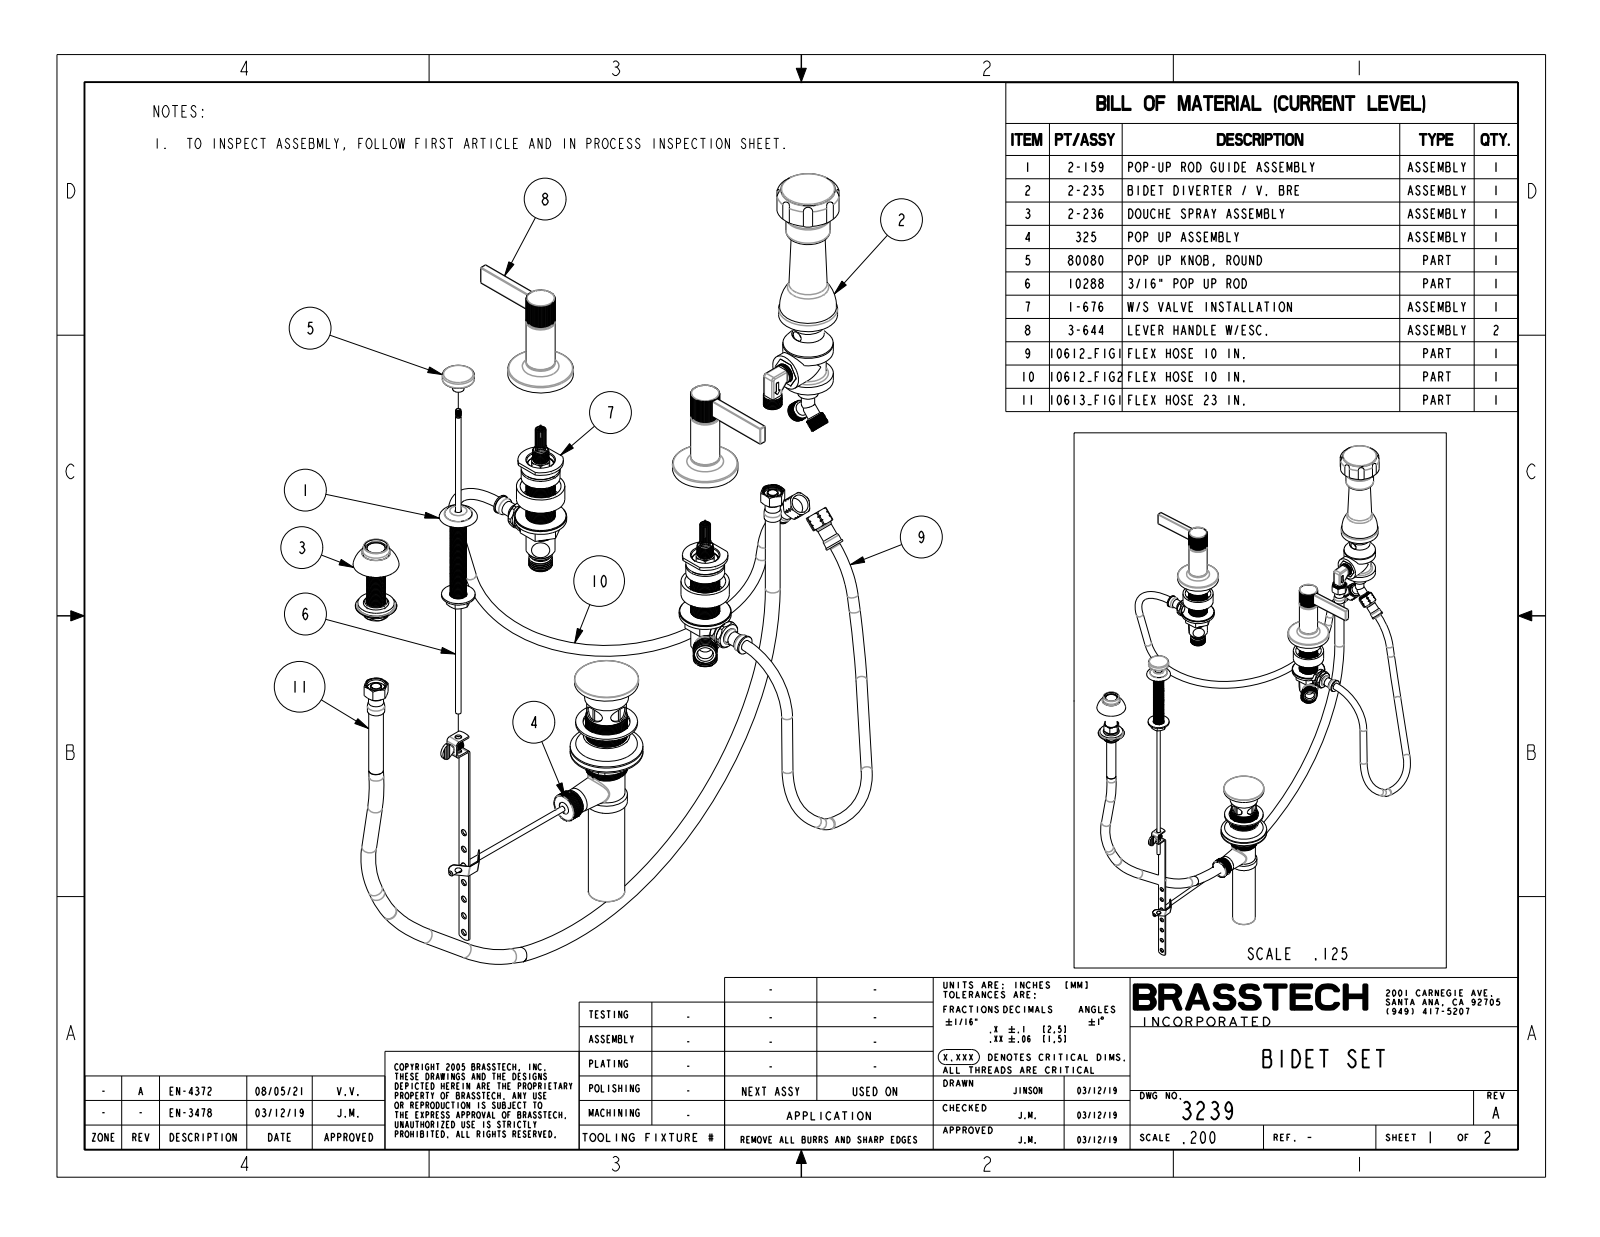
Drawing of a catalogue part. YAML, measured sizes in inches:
part_name: "10078; 2-159_ASM; 91093; 10600 (+8 more)"
step_written_by: "CREO PARAMETRIC BY PTC INC, 2018400 (CONFIG_CONTROL_DESIGN)"
units: inches
bodies: {solids: 39, faces: 3429, planar: 1238, cylindrical: 1397, other: 794}
overall_size: [22.855, 13.6, 5.373]
volume: 10.96
surface_area: 279.4
round_holes:
  - {diameter: 0.11, count: 4}
  - {diameter: 0.15, count: 3}
  - {diameter: 0.6, count: 3}
  - {diameter: 0.14, count: 2}
  - {diameter: 0.275, count: 2}
  - {diameter: 0.335, count: 2}
  - {diameter: 0.358, count: 2}
  - {diameter: 0.375, count: 2}
  - {diameter: 0.383, count: 2}
  - {diameter: 0.397, count: 2}
  - {diameter: 0.4, count: 2}
  - {diameter: 0.42, count: 2}
round_bosses_or_shafts:
  - {diameter: 0.138, count: 4}
  - {diameter: 2.25, count: 2}
  - {diameter: 1.812, count: 2}
  - {diameter: 1, count: 2}
  - {diameter: 0.85, count: 2}
  - {diameter: 0.73, count: 2}
  - {diameter: 0.572, count: 2}
  - {diameter: 0.52, count: 2}
partial_cylinders:
  - {radius: 0.05, count: 30}
  - {radius: 0.111, count: 30}
  - {radius: 0.184, count: 30}
  - {radius: 0.02, count: 20}
  - {radius: 0.01, count: 12}
  - {radius: 0.042, count: 12}
  - {radius: 0.21, count: 8}
  - {radius: 0.1, count: 6}
face_to_face_distances: [0.25, 0.705, 2.321, 0.055, 0.175, 3.201, 3.026, 0.624, 0.25, 0.5]
hole_center_spacings: [0.335, 8.335, 8.944, 9.099, 9.849, 9.99, 12.649, 12.759]
